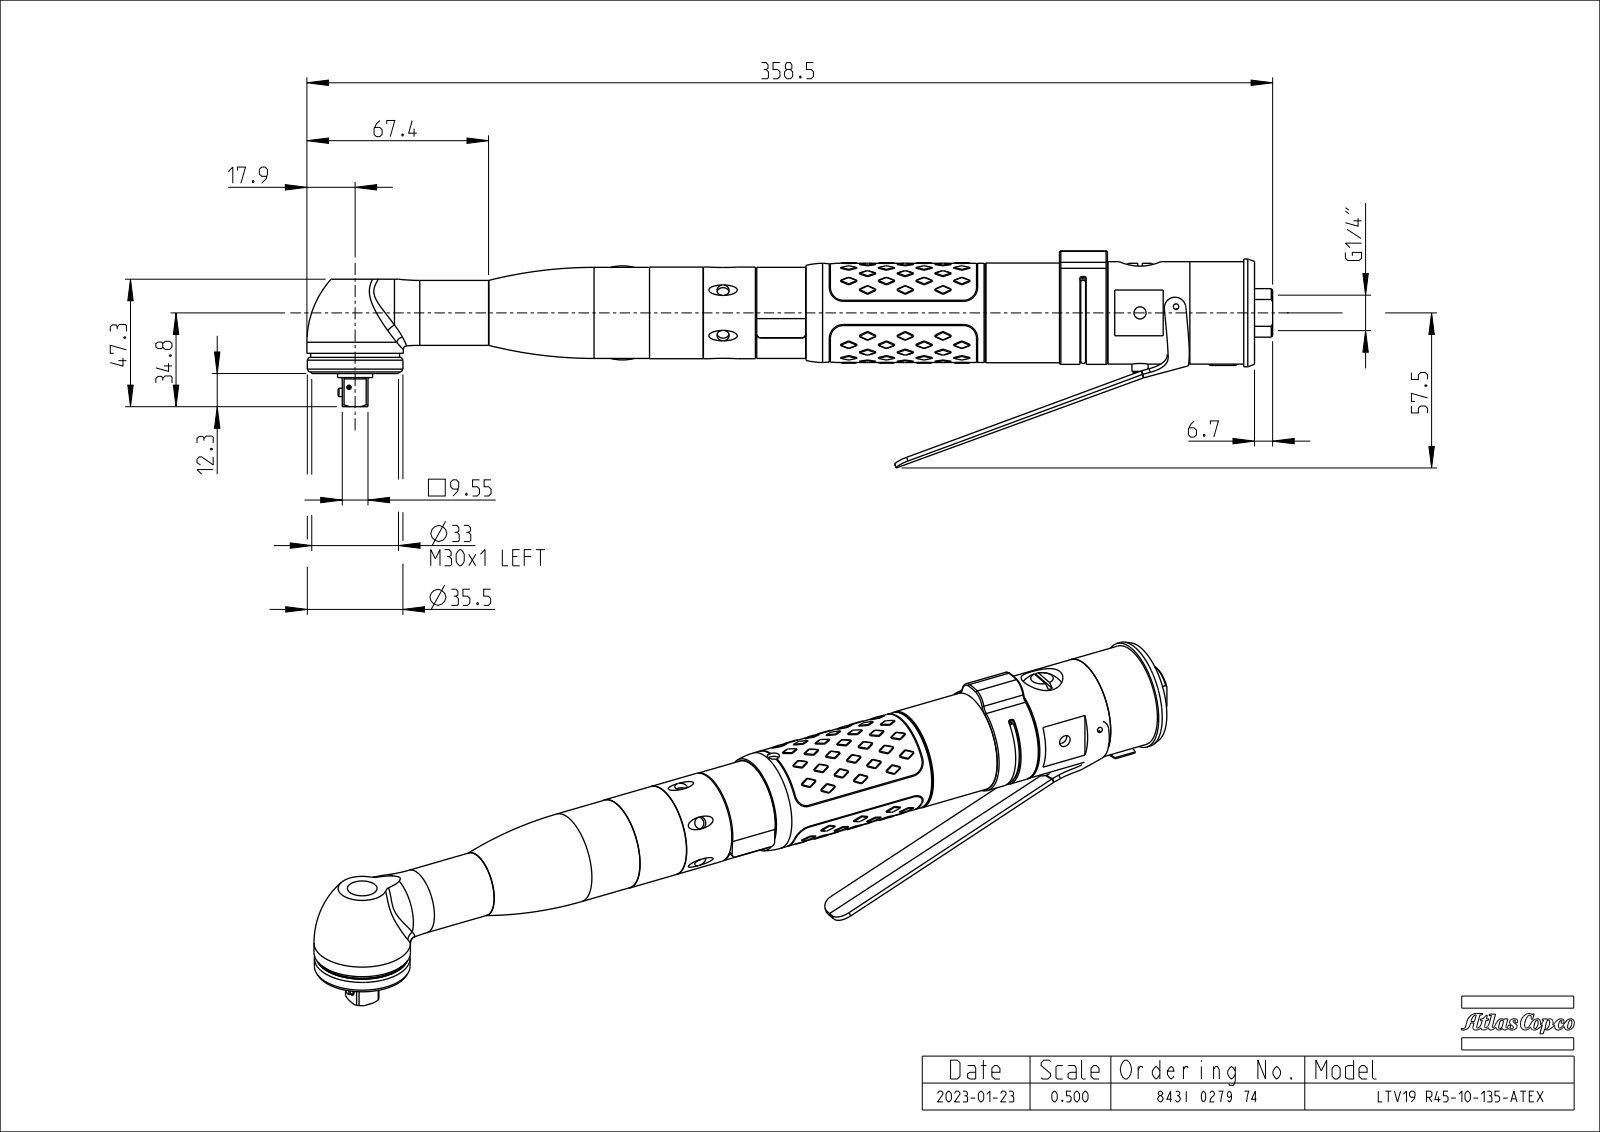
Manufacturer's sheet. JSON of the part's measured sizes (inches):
{"step_written_by": "CREO PARAMETRIC BY PTC INC, 2020281 (CONFIG_CONTROL_DESIGN)", "units": "inches", "bodies": {"solids": 2, "faces": 1289, "planar": 100, "cylindrical": 276, "other": 913}, "overall_size": [14.115, 3.171, 1.575], "volume_in3": 20.21, "surface_area_in2": 84.67, "round_holes": [[0.118, 12], [0.177, 9], [0.61, 2], [0.059, 1], [0.071, 1], [0.122, 1], [0.451, 1], [0.535, 1], [0.728, 1], [1.264, 1], [1.307, 1], [1.331, 1]], "round_bosses_or_shafts": [[1.339, 2], [1.575, 1], [1.504, 1], [1.496, 1], [1.457, 1], [1.449, 1], [1.433, 1], [1.409, 1]], "partial_cylinders_radius": [[0.02, 11], [0.031, 6], [0.008, 4], [0.028, 2], [0.039, 2], [0.045, 2], [0.059, 2], [0.157, 2]], "face_to_face_distances": [0.079, 0.059, 4.122, 1.339, 0.02, 2.142, 1.378, 1.083, 0.157, 2.15], "hole_center_spacings": [0.63, 0.891, 1.217, 0.326, 1.091, 0.326, 0.453, 0.64]}
